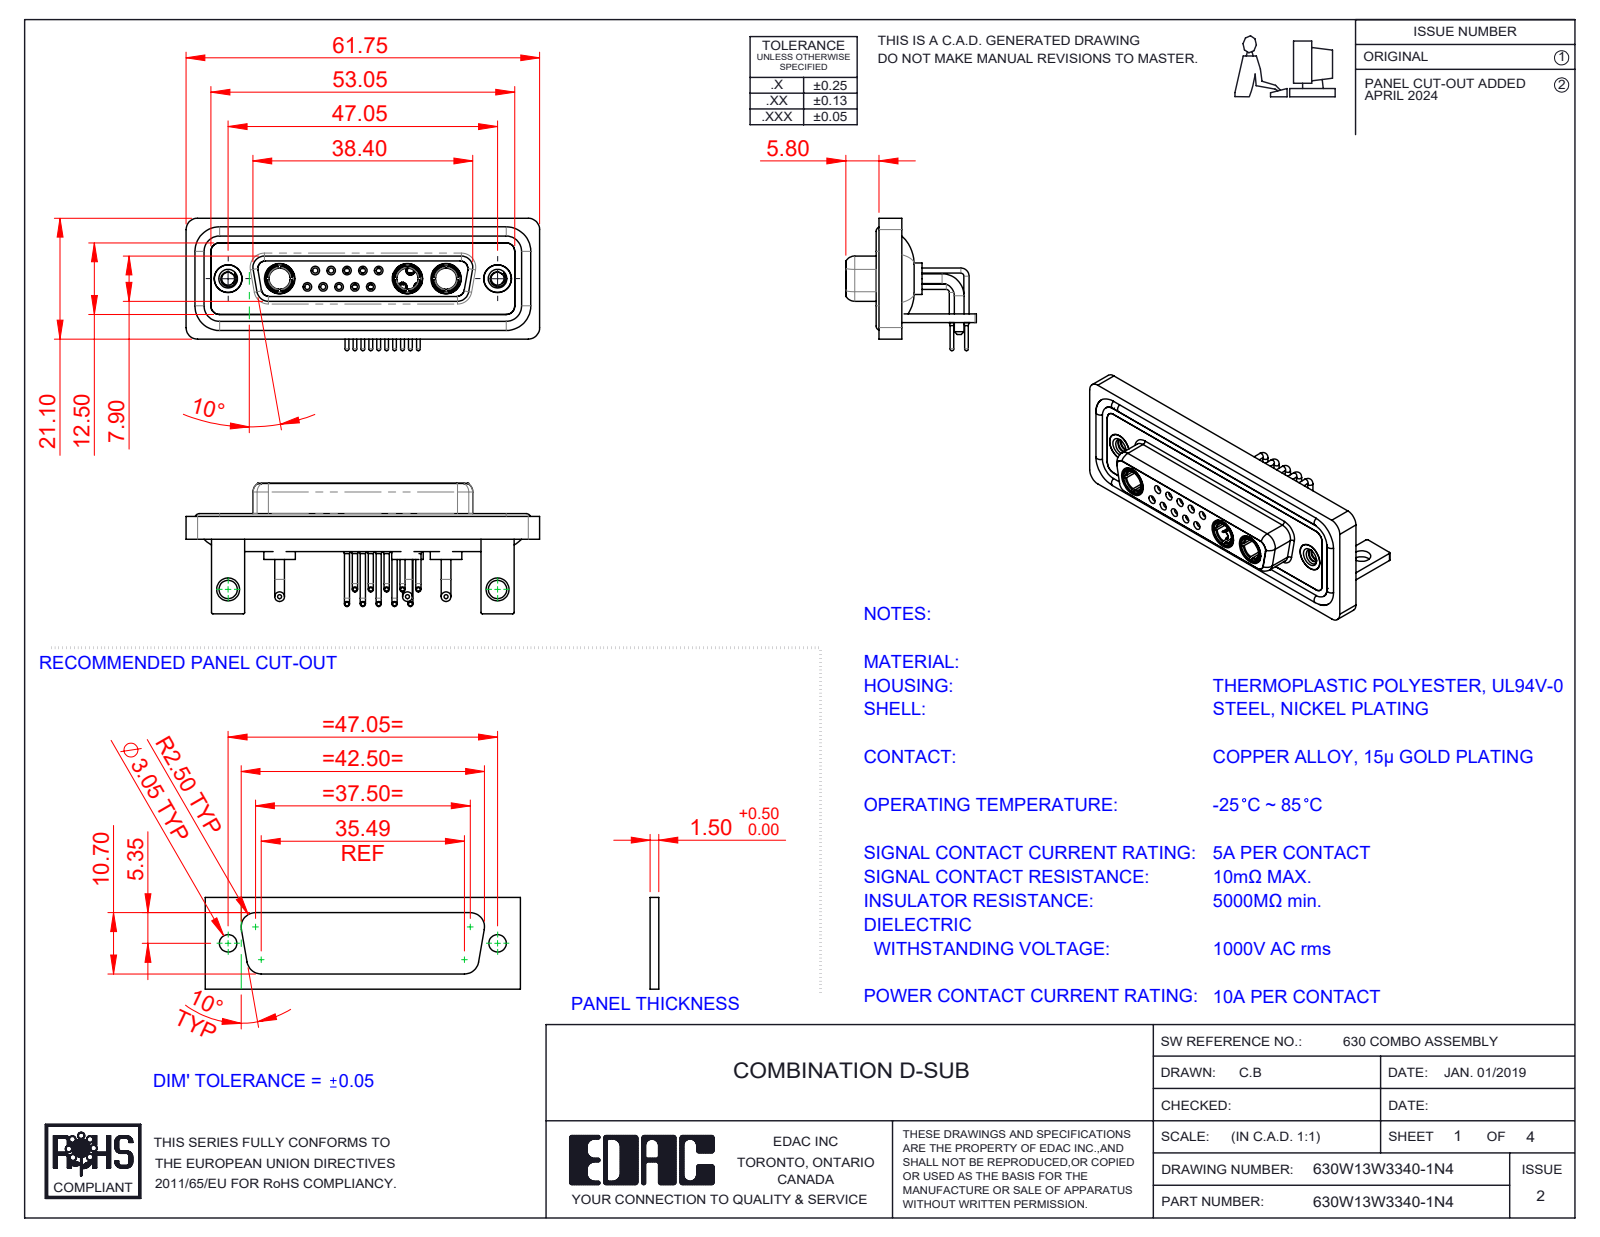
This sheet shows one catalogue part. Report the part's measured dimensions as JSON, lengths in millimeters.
{"part_name": "Power Socket_10A RA; 630Combo Shell Rear_25 Contacts; 630Combo Contact Row 2_50 Contacts; 630Combo Housing_13W3 (+6 more)", "step_written_by": "SolidWorks 2023 (CONFIG_CONTROL_DESIGN)", "units": "millimeters", "bodies": {"solids": 25, "faces": 1198, "planar": 362, "cylindrical": 517, "other": 319}, "overall_size": [61.75, 23.12, 22.8], "volume_mm3": 8664, "surface_area_mm2": 14880, "round_holes": [[0.9, 10], [1.1, 10], [1.5, 10], [2, 10], [1.6, 5], [1.7, 5], [4.85, 5], [3.7, 3], [5.3, 3], [2.26, 2], [3.2, 2], [4, 2]], "round_bosses_or_shafts": [[0.9, 15], [1.6, 12], [0.65, 10], [1.7, 6], [2, 5], [1.5, 5], [5.5, 3], [5.2, 3]], "partial_cylinders_radius": [[2, 19], [1.5, 18], [0.25, 16], [1.35, 8], [1.6, 8], [0.5, 5], [0.6, 4], [0.65, 4]], "face_to_face_distances": [0.4, 1.8, 2.9, 1.5, 3.7, 4.1, 1.1, 1.4, 1.6, 3.1], "hole_center_spacings": [3.16, 2.77, 5.54, 5.04, 8.31, 5.03, 7.49, 11.08]}
